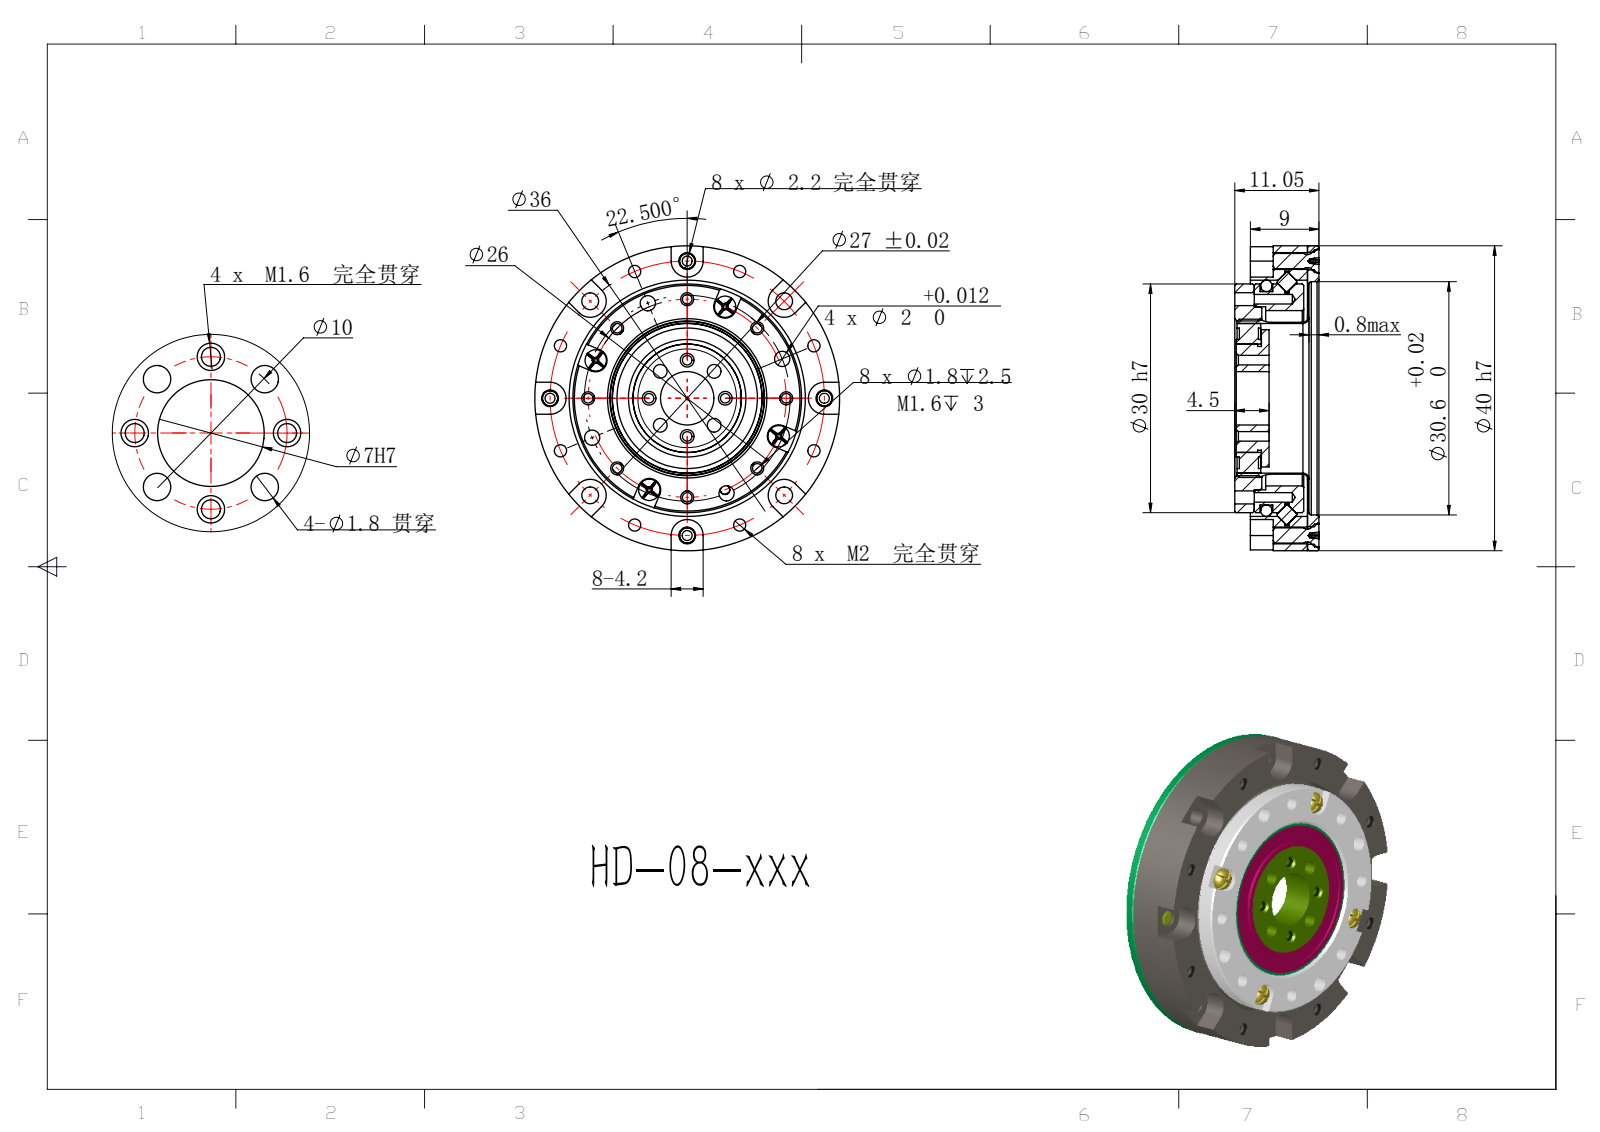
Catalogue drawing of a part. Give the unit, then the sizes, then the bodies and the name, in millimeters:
Units: millimetres
Overall size (bounding box): 40 × 40 × 11.05
Round holes (diameter × count): ⌀1.25 ×17, ⌀2.3 ×16, ⌀1.7 ×12, ⌀1.6 ×8, ⌀2.2 ×8, ⌀1.8 ×4, ⌀2 ×4, ⌀3.2 ×4, ⌀1.62 ×1, ⌀7 ×1, ⌀14.22 ×1, ⌀18.43 ×1
Round bosses / shafts (diameter × count): ⌀2 ×50, ⌀2.8 ×5, ⌀1.6 ×5, ⌀3 ×4, ⌀1.73 ×4, ⌀40 ×1, ⌀30 ×1, ⌀28 ×1
Partial cylindrical surfaces — rounded edges, fillets, slot ends (radius × count): R2.1 ×8, R1.5 ×5
Main face-to-face distances: 0.5, 1.5, 7, 7.5, 9, 8.5, 1.45, 4.55, 1.95, 1.31
Hole centre spacings: 13.93, 13, 18, 16.91, 18.68, 22.2, 5, 7.07
Volume: 7 840 mm³ · Surface area: 13 673 mm²
Bodies: 63 solids, 780 faces (379 planar, 188 cylindrical, 213 other)
Part name (STEP PRODUCT): HD-08-xxx; M1.6-??_??; HD-08-??; HD-08-????_?? <1> (+8 more)
STEP written by: ONSHAPE BY PTC INC, 1.201 (AP242_MANAGED_MODEL_BASED_3D_ENGINEERING_MIM_LF)
